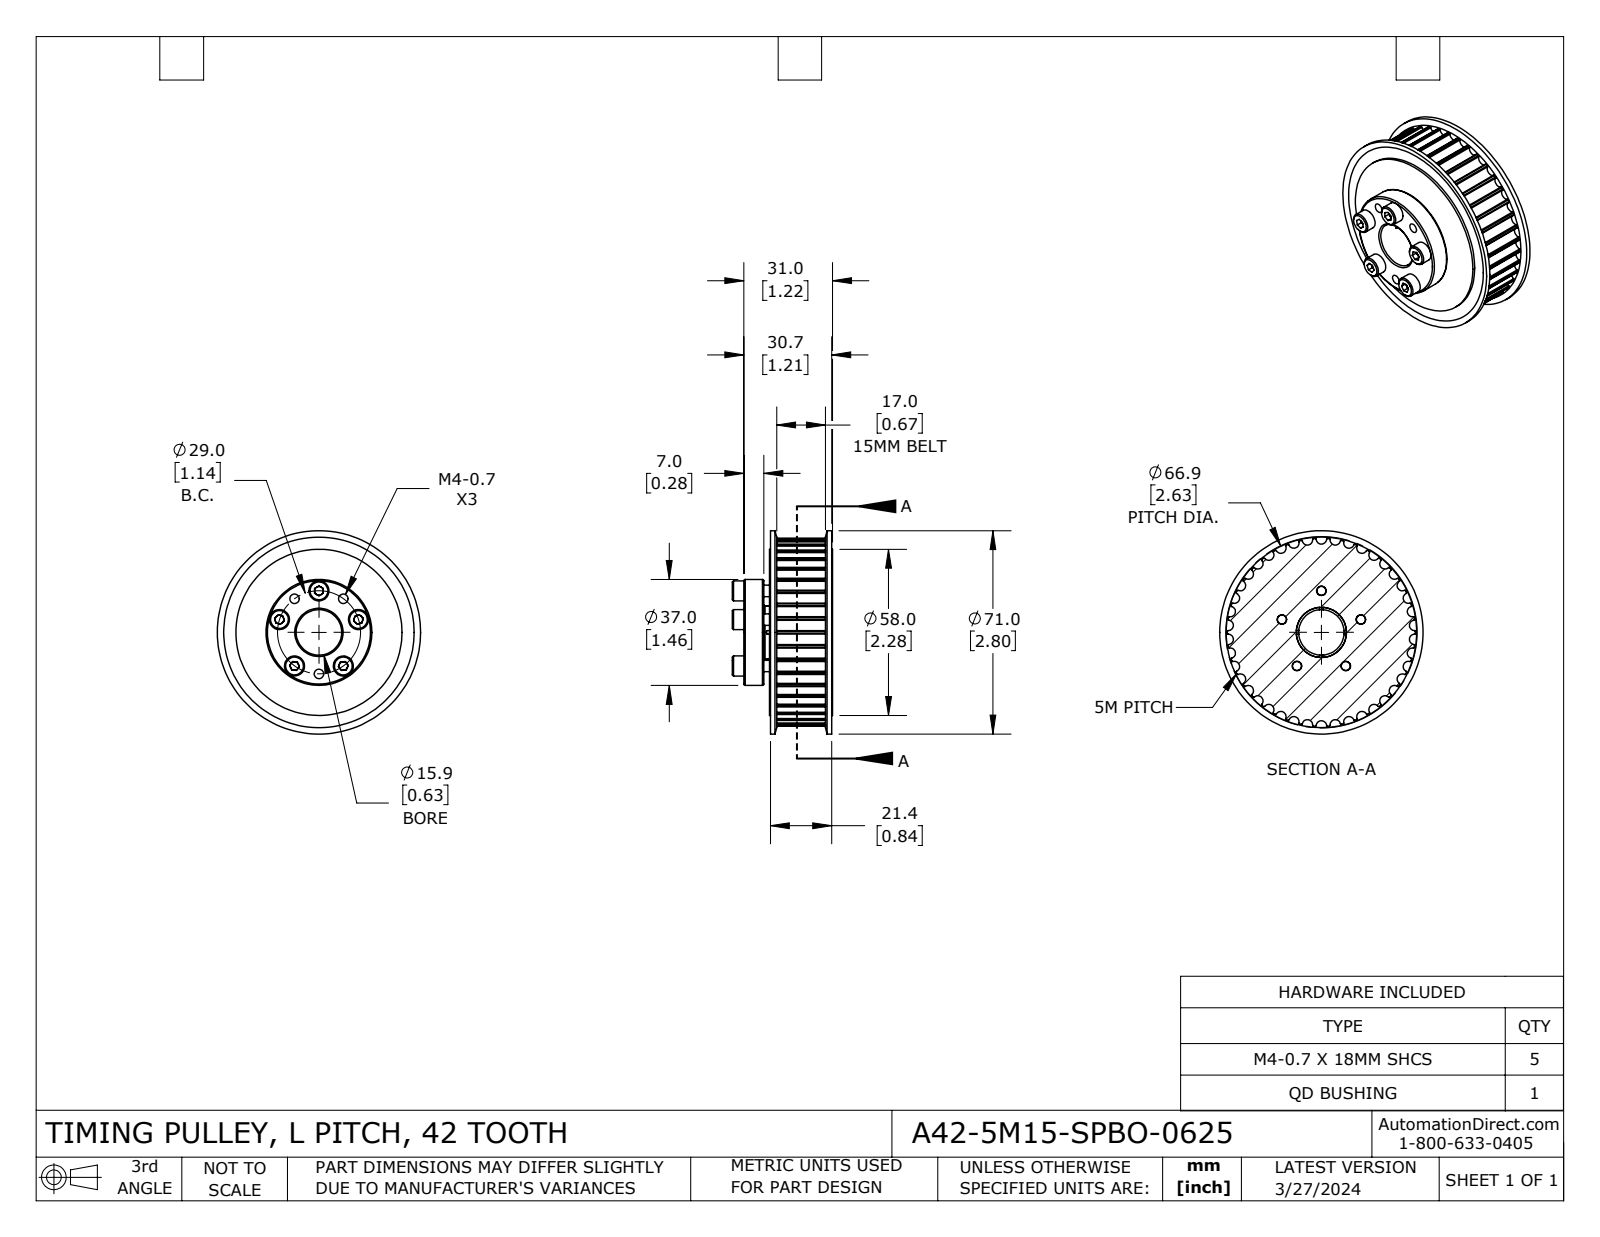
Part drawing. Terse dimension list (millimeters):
name: A42-5M15-SPBO-0625
written by: SolidWorks 2021 (CONFIG_CONTROL_DESIGN)
unit: mm
bodies: 9 solids, 444 faces (101 planar, 277 cylindrical, 66 other)
size: 71 × 71 × 35
volume: 73 059 mm³; area: 27 315 mm²
holes: 8× ⌀3.3, 5× ⌀4.5, 1× ⌀15.88, 1× ⌀18.47, 1× ⌀58
bosses: 5× ⌀7, 5× ⌀4, 1× ⌀71, 1× ⌀37
rounds: 84× R0.3, 42× R1.82, 1× R32.85
face distances: 2.5, 19.5, 22, 0.9, 21.1, 1.6, 18.6, 17, 9, 20.2
hole spacings: 14.5, 27.58, 8.96, 23.46, 17.05, 29, 17.04
